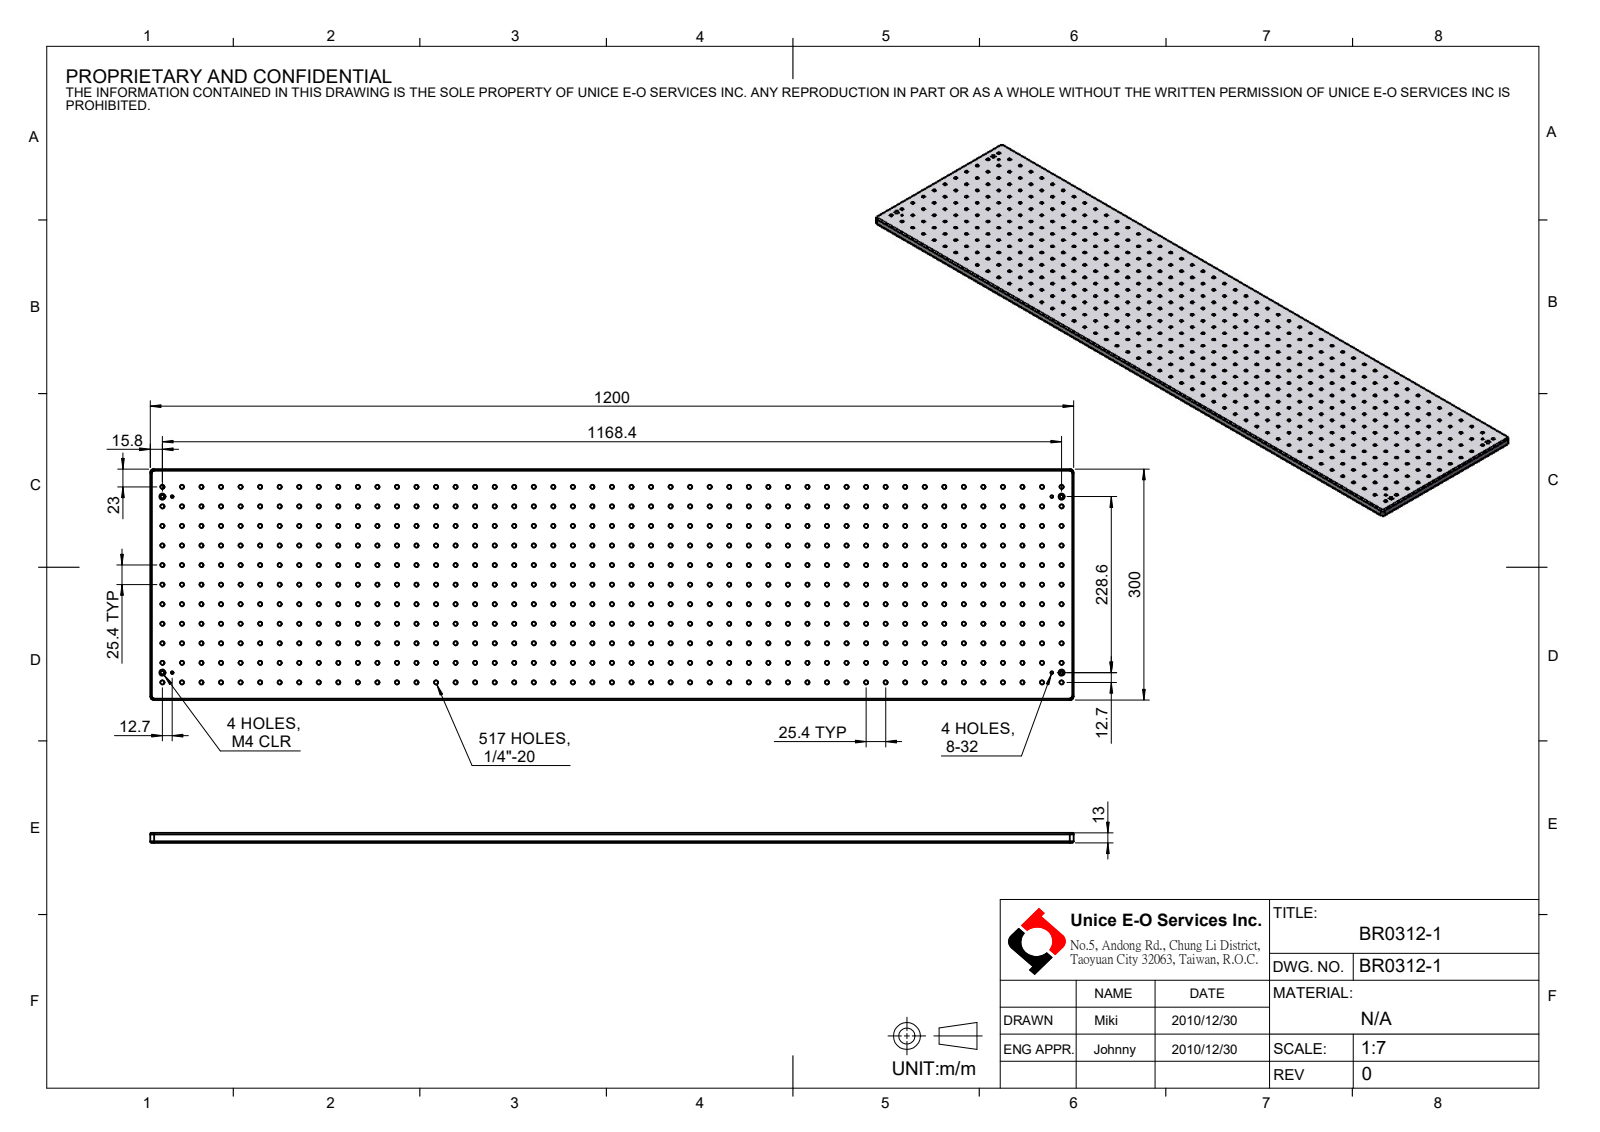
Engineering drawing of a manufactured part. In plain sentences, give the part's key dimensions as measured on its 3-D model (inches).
The part is named "BR0312-1". Its 3-D file was written by "SolidWorks 2016 (CONFIG_CONTROL_DESIGN)". It is 1 solid with 1088 faces: 10 planar, 1070 cylindrical and 8 other. Overall it measures 47.244 by 11.811 by 0.512 inches. Its volume is 276.7 cubic inches and its surface area 1 305 square inches. Round holes: 517 of diameter 0.201, 4 of diameter 0.136, 4 of diameter 0.177, 4 of diameter 0.315. Partial cylindrical surfaces (rounded edges, fillets, slot ends): 8 of radius 0.079, 4 of radius 0.197. The main face-to-face distances are 0.512, 11.811, 47.244, 0.276, 0.236. The hole center spacings are 1, 2, 3, 5, 4, 10.05, 10.198, 10.44.
